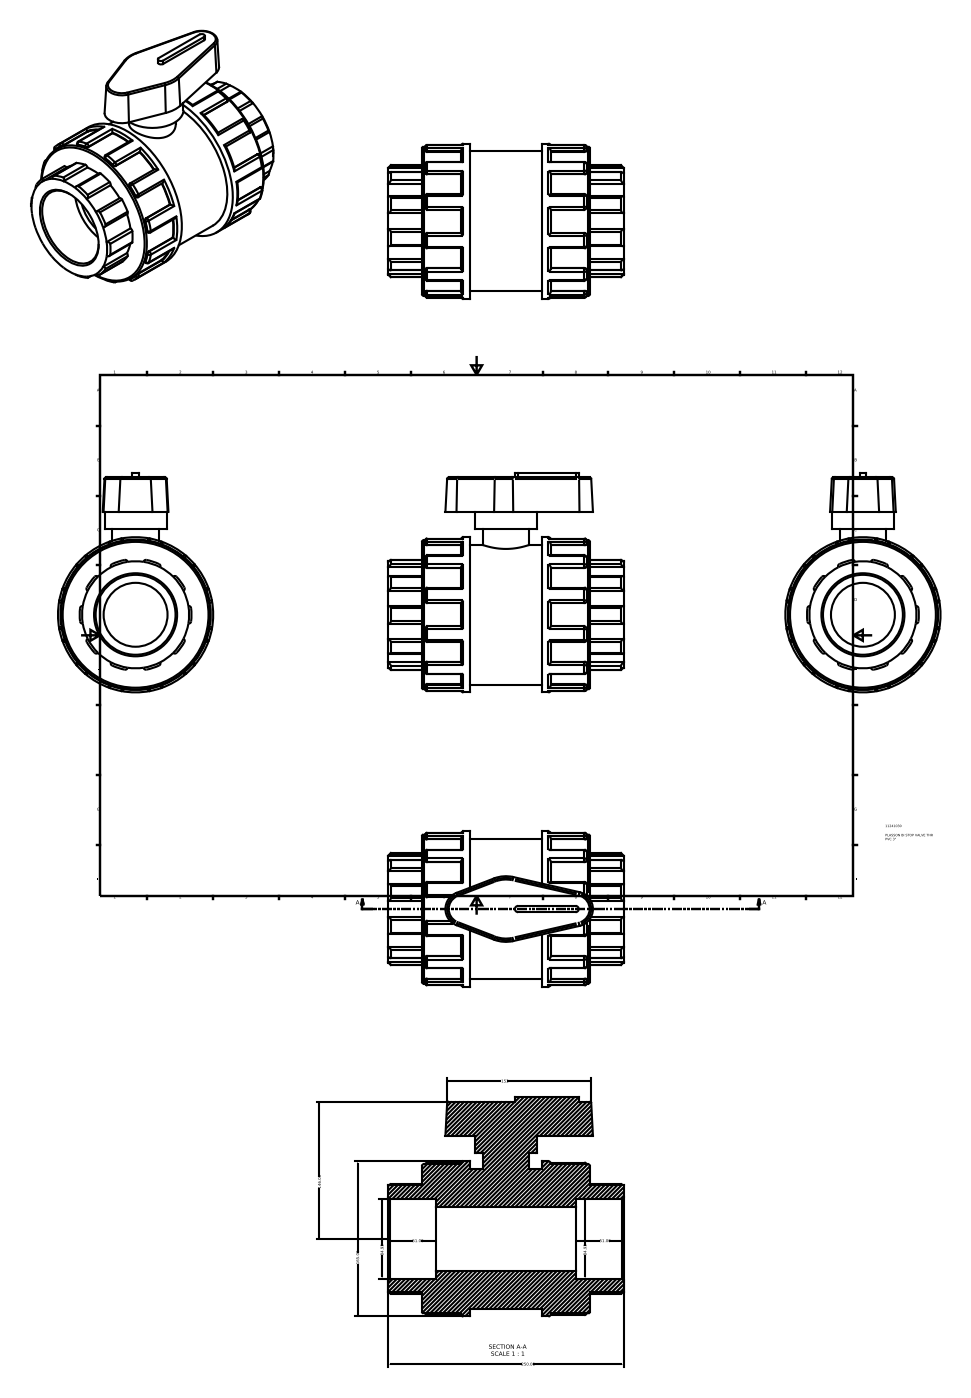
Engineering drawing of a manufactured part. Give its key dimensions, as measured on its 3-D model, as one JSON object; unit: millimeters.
{"part_name": "11241030", "step_written_by": "Autodesk Inventor 2015 (AUTOMOTIVE_DESIGN)", "units": "millimeters", "bodies": {"solids": 1, "faces": 434, "planar": 114, "cylindrical": 192, "other": 128}, "overall_size": [250, 232.88, 165], "volume_mm3": 3427000, "surface_area_mm2": 250312, "round_holes": [[67.94, 1], [84.93, 1]], "round_bosses_or_shafts": [[165, 1], [158.4, 1], [148.5, 1], [66, 1], [49.5, 1]], "partial_cylinders_radius": [[2.55, 68], [1.7, 4], [3.3, 2], [56.9, 1], [59.45, 1]], "face_to_face_distances": [51, 35.7, 163.3, 178.6, 127.6, 86.7, 214.3, 36.5, 199, 15.3]}
